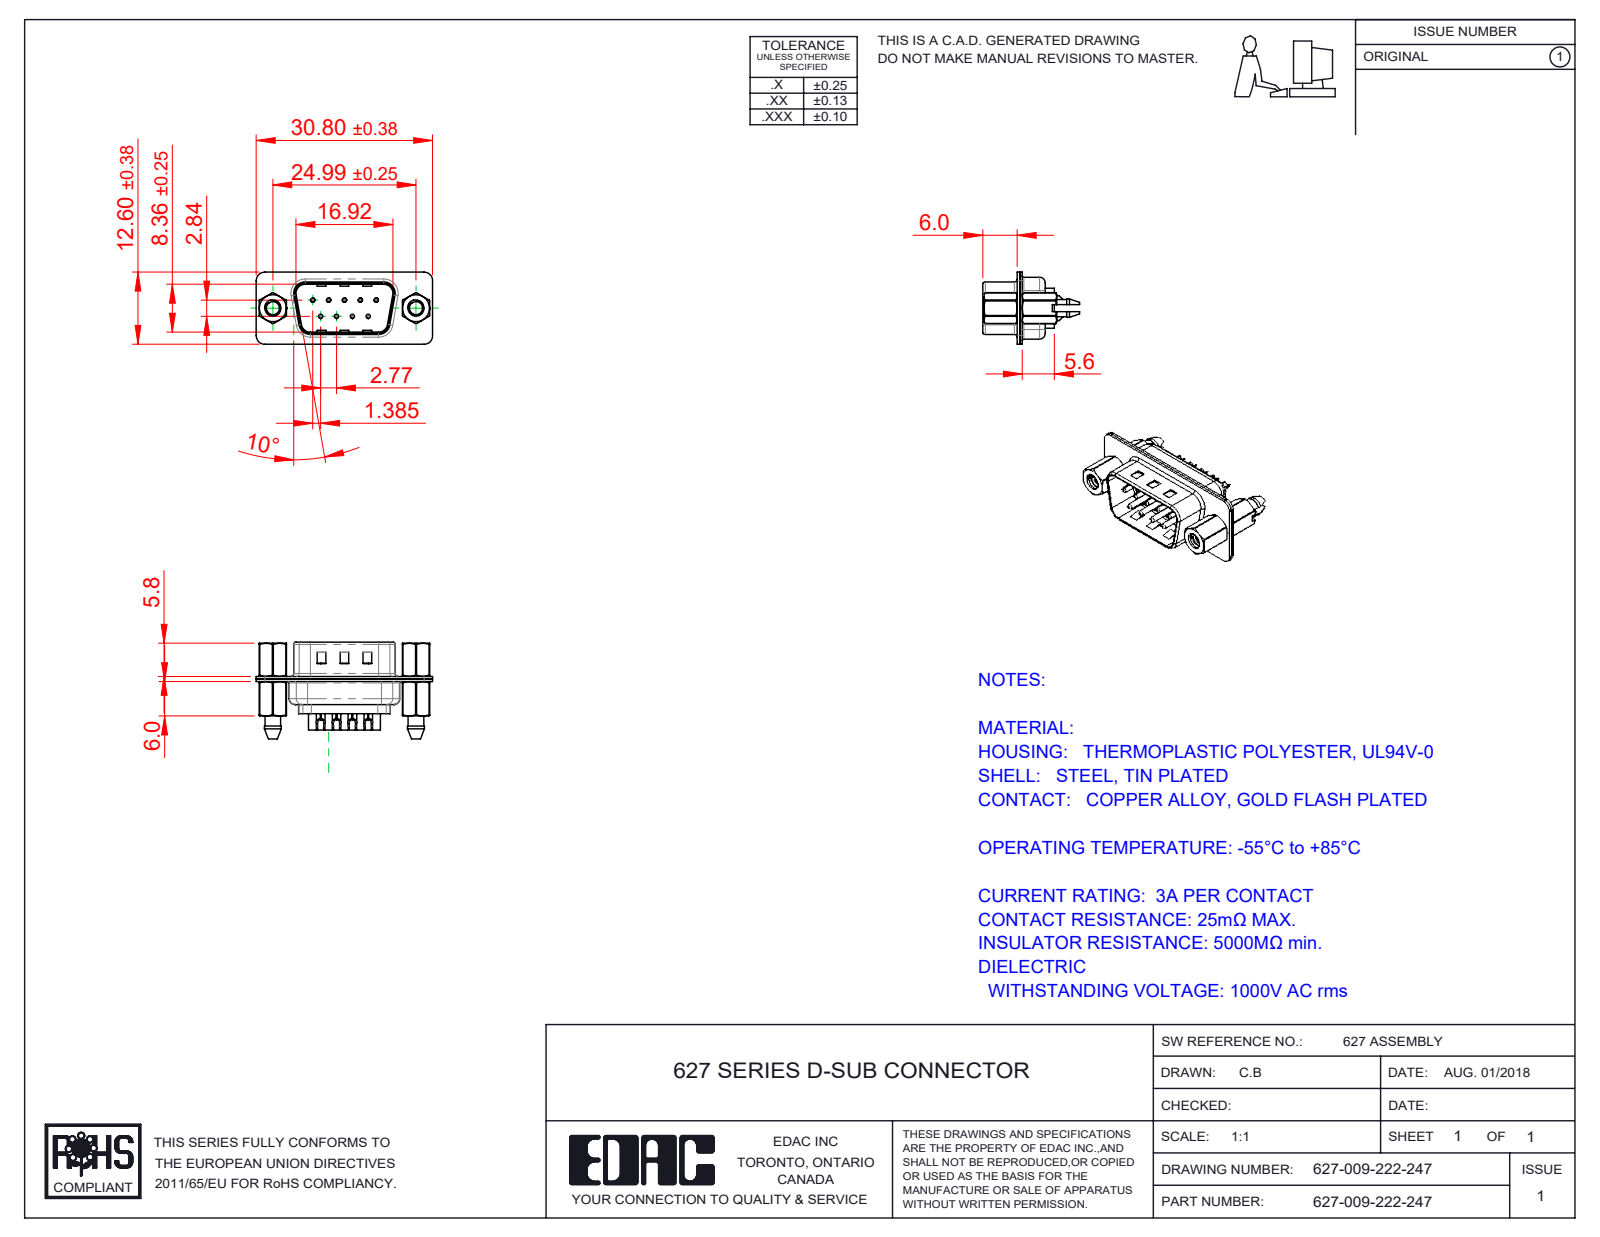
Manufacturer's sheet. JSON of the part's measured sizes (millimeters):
{"part_name": "627 Contact Row 1_22L; 627 Contact Row 2_22L; 627 Shell Rear_09 Contacts; 627 4-40 Threaded Boardlock_LP (+4 more)", "step_written_by": "SolidWorks 2020 (CONFIG_CONTROL_DESIGN)", "units": "millimeters", "bodies": {"solids": 16, "faces": 1080, "planar": 287, "cylindrical": 494, "other": 299}, "overall_size": [30.8, 16.9, 12.6], "volume_mm3": 1642, "surface_area_mm2": 4727, "round_holes": [[0.35, 9], [1.1, 9], [1.6, 9], [2.26, 2], [2.29, 2], [4, 2], [4.8, 2]], "round_bosses_or_shafts": [[2, 9], [1.5, 9], [0.75, 9], [4.9, 2], [2.79, 2]], "partial_cylinders_radius": [[1.5, 20], [2, 12], [1.6, 10], [0.5, 8], [1, 6], [0.25, 4], [0.6, 4], [0.65, 4]], "face_to_face_distances": [0.45, 0.4, 0.9, 0.82, 9.58, 1.4, 4.76, 8.76, 6.5, 0.5], "hole_center_spacings": [3.16, 2.77, 5.54, 5.03, 5.04, 8.31, 7.48, 7.49]}
